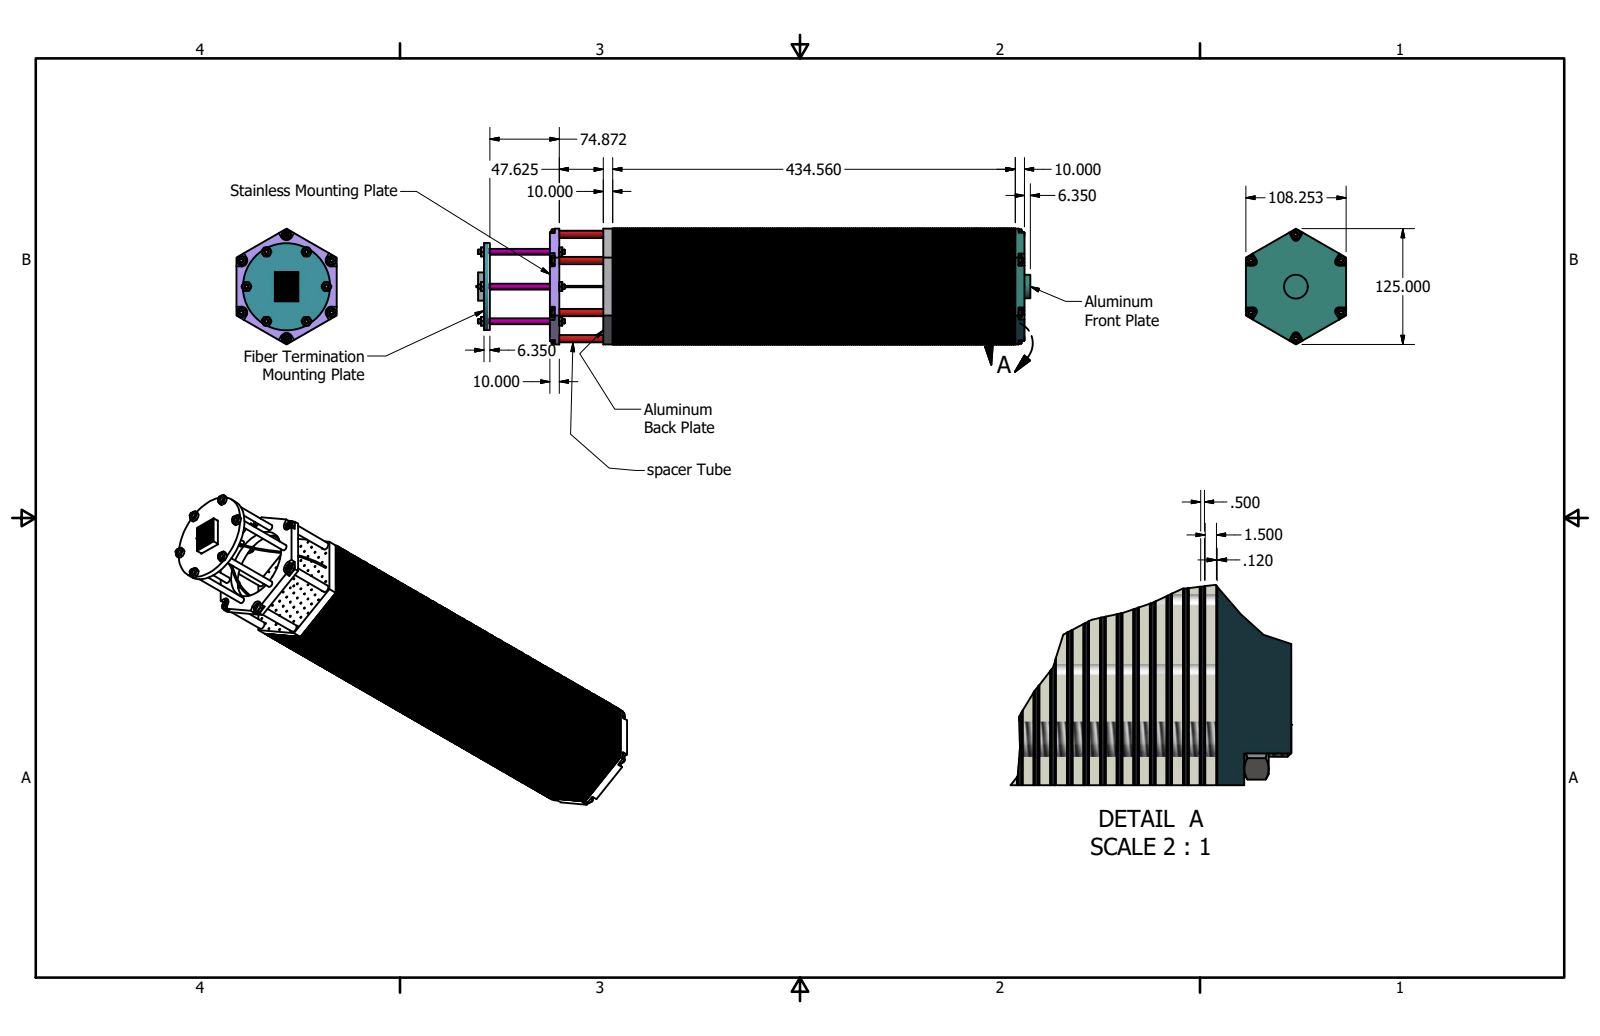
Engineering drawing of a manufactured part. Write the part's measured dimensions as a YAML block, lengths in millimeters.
part_name: "FrontEndPlate-ver1; Paper-ver1; Scintillator-ver1; Lead-ver1 (+8 more)"
step_written_by: "Autodesk Inventor 2016 (AUTOMOTIVE_DESIGN)"
units: millimeters
bodies: {solids: 815, faces: 86770, planar: 4320, cylindrical: 55680, other: 26770}
overall_size: [590.56, 125, 108.25]
volume: 4569000
surface_area: 15970000
round_holes:
  - {diameter: 1.5, count: 97}
  - {diameter: 3, count: 6}
face_to_face_distances: [2.24, 4.48, 1.62, 2.36, 3.86, 6.72, 2.12, 0.62, 4.6, 6.1]
hole_center_spacings: [10.82, 21.64, 10.83, 28.64, 18.74, 28.63, 18.75, 18.76]
